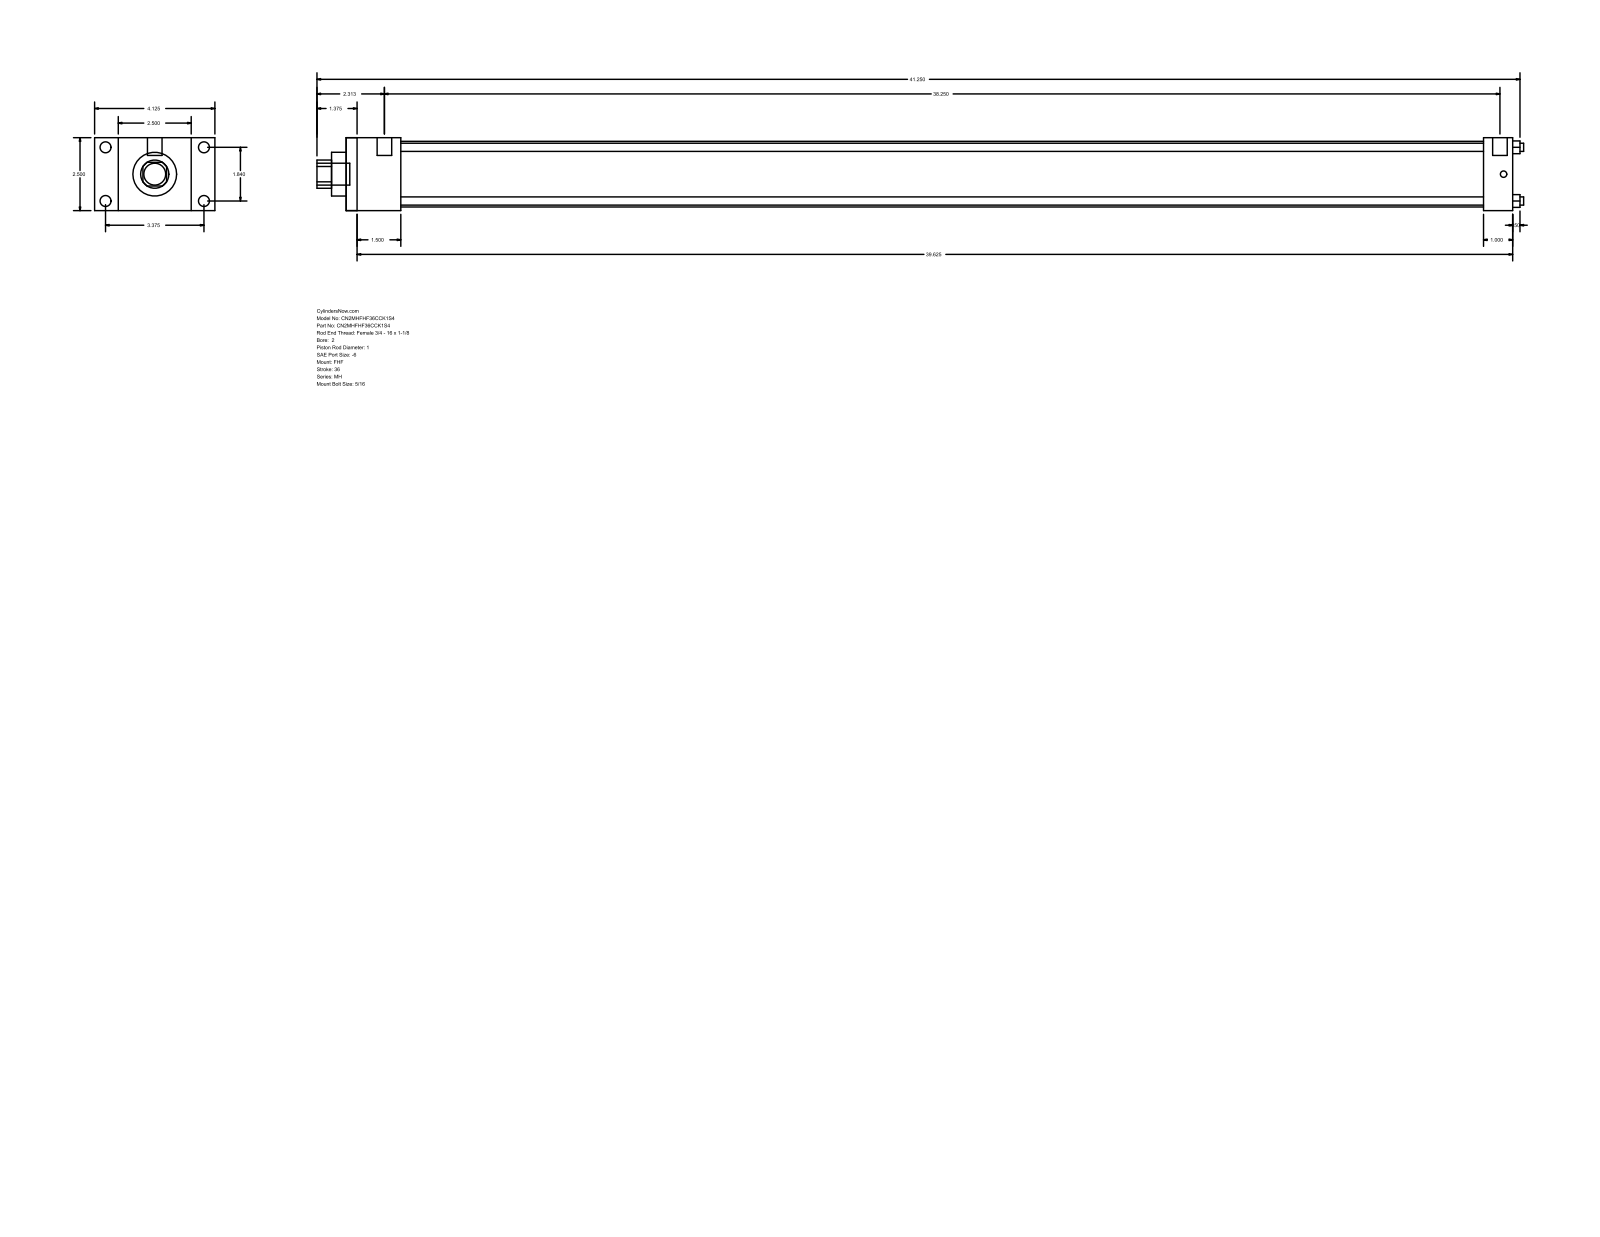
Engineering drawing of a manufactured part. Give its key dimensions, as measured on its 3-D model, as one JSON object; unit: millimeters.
{"part_name": "MH_FHF__0200_1", "step_written_by": "GSSL Pune (CONFIG_CONTROL_DESIGN)", "units": "millimeters", "bodies": {"solids": 0, "faces": 88, "planar": 60, "cylindrical": 28, "other": 0}, "overall_size": [1050.92, 104.78, 63.5], "round_holes": [[7.14, 4], [25.4, 1], [38.1, 1], [57.15, 1]], "round_bosses_or_shafts": [[9.53, 4], [5.56, 4], [12.7, 2], [19.05, 1]], "partial_cylinders_radius": [[12.29, 1]], "face_to_face_distances": [63.5, 1016, 47.63, 968.37, 20.64, 84.14, 104.78, 25.4, 990.6, 942.97], "hole_center_spacings": [33.05, 46.74, 66.1]}
